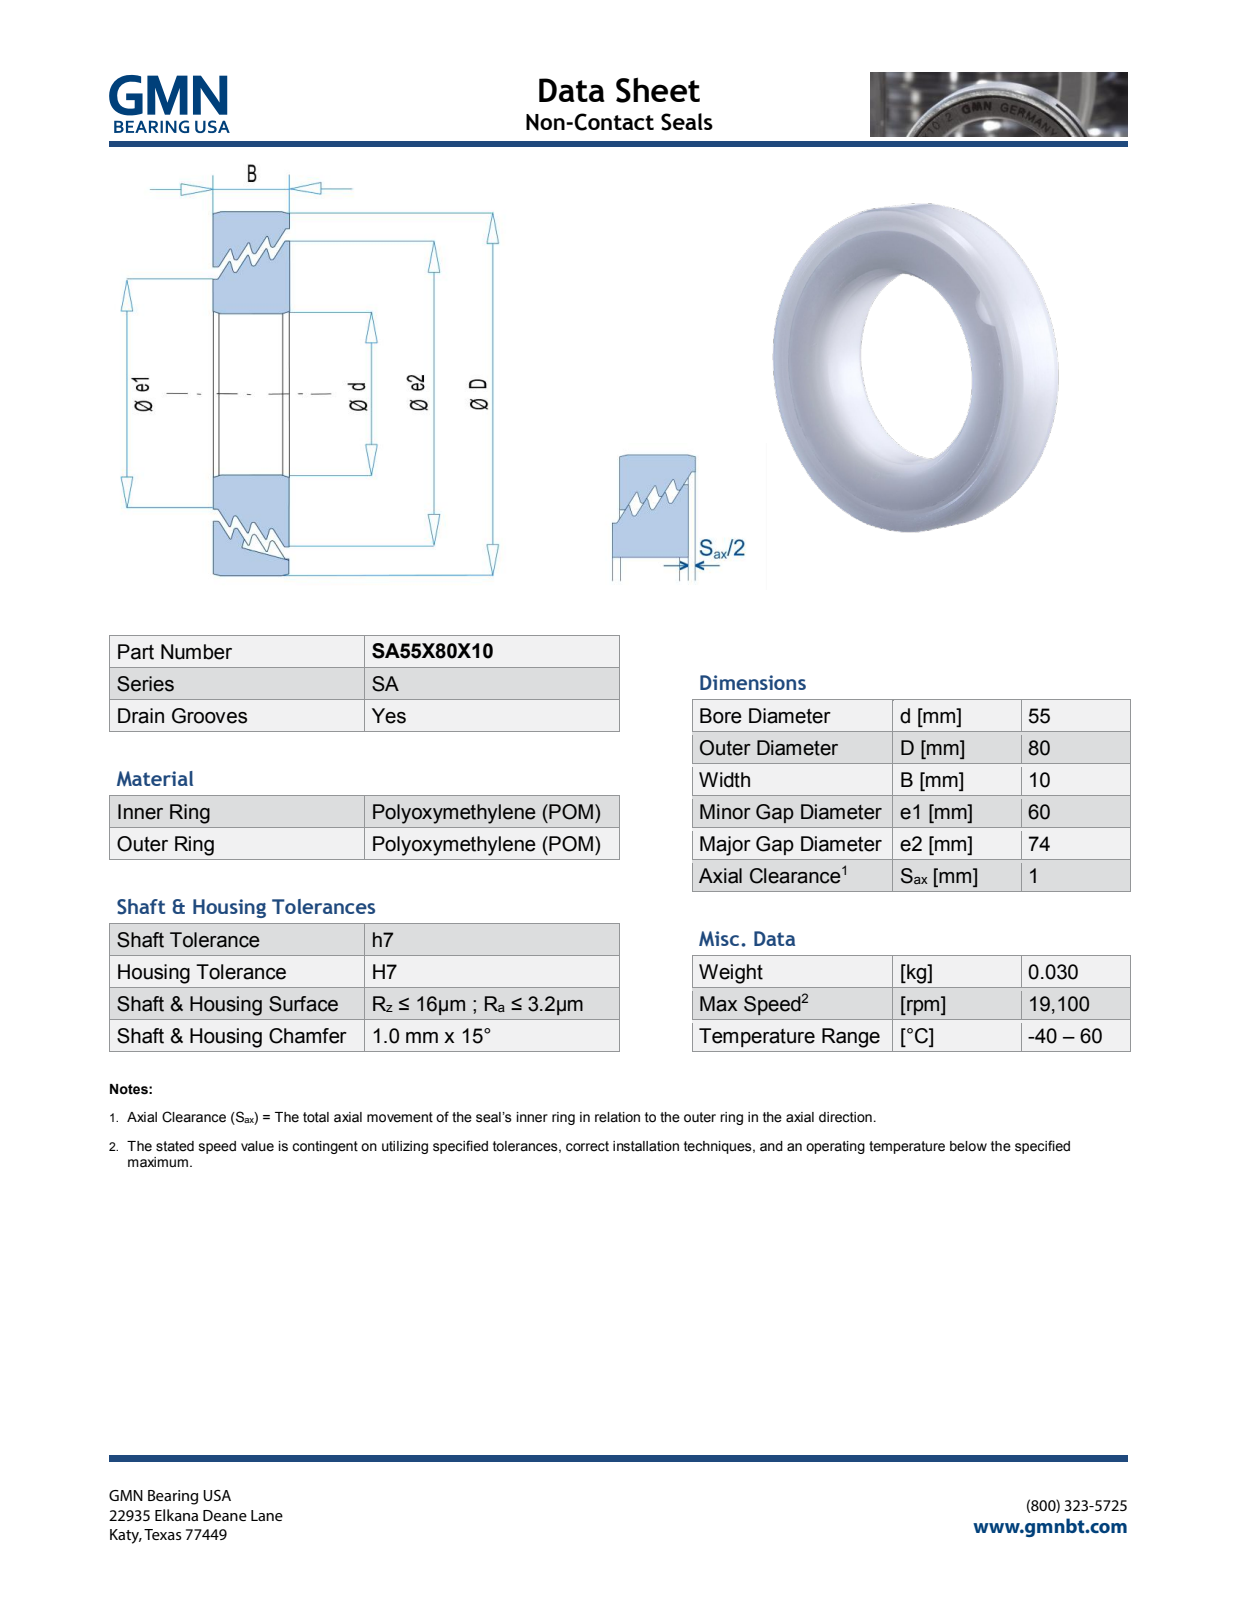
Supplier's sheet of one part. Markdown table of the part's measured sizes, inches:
| quantity | value |
| --- | --- |
| part name | SA55X80X10_PRT |
| STEP written by | PRO/ENGINEER BY PARAMETRIC TECHNOLOGY CORPORATION, 2013150 (AUTOMOTIVE_DESIGN) |
| units | inches |
| bodies | 2 solids, 697 faces (624 planar, 13 cylindrical, 60 other) |
| overall size | 3.15 × 3.15 × 0.396 |
| volume | 1.502 in³ |
| surface area | 27.11 in² |
| round holes (diameter × count) | 2.165 × 1, 2.426 × 1, 2.978 × 1 |
| round bosses / shafts (diameter × count) | 3.15 × 1, 2.913 × 1, 2.362 × 1 |
| partial cylindrical surfaces (radius × count) | 0.236 × 1 |
| main face-to-face distances | 0.394, 0.396, 0.215, 0.212, 0.181, 0.013, 0.013, 0.102, 0.089, 0.072 |
